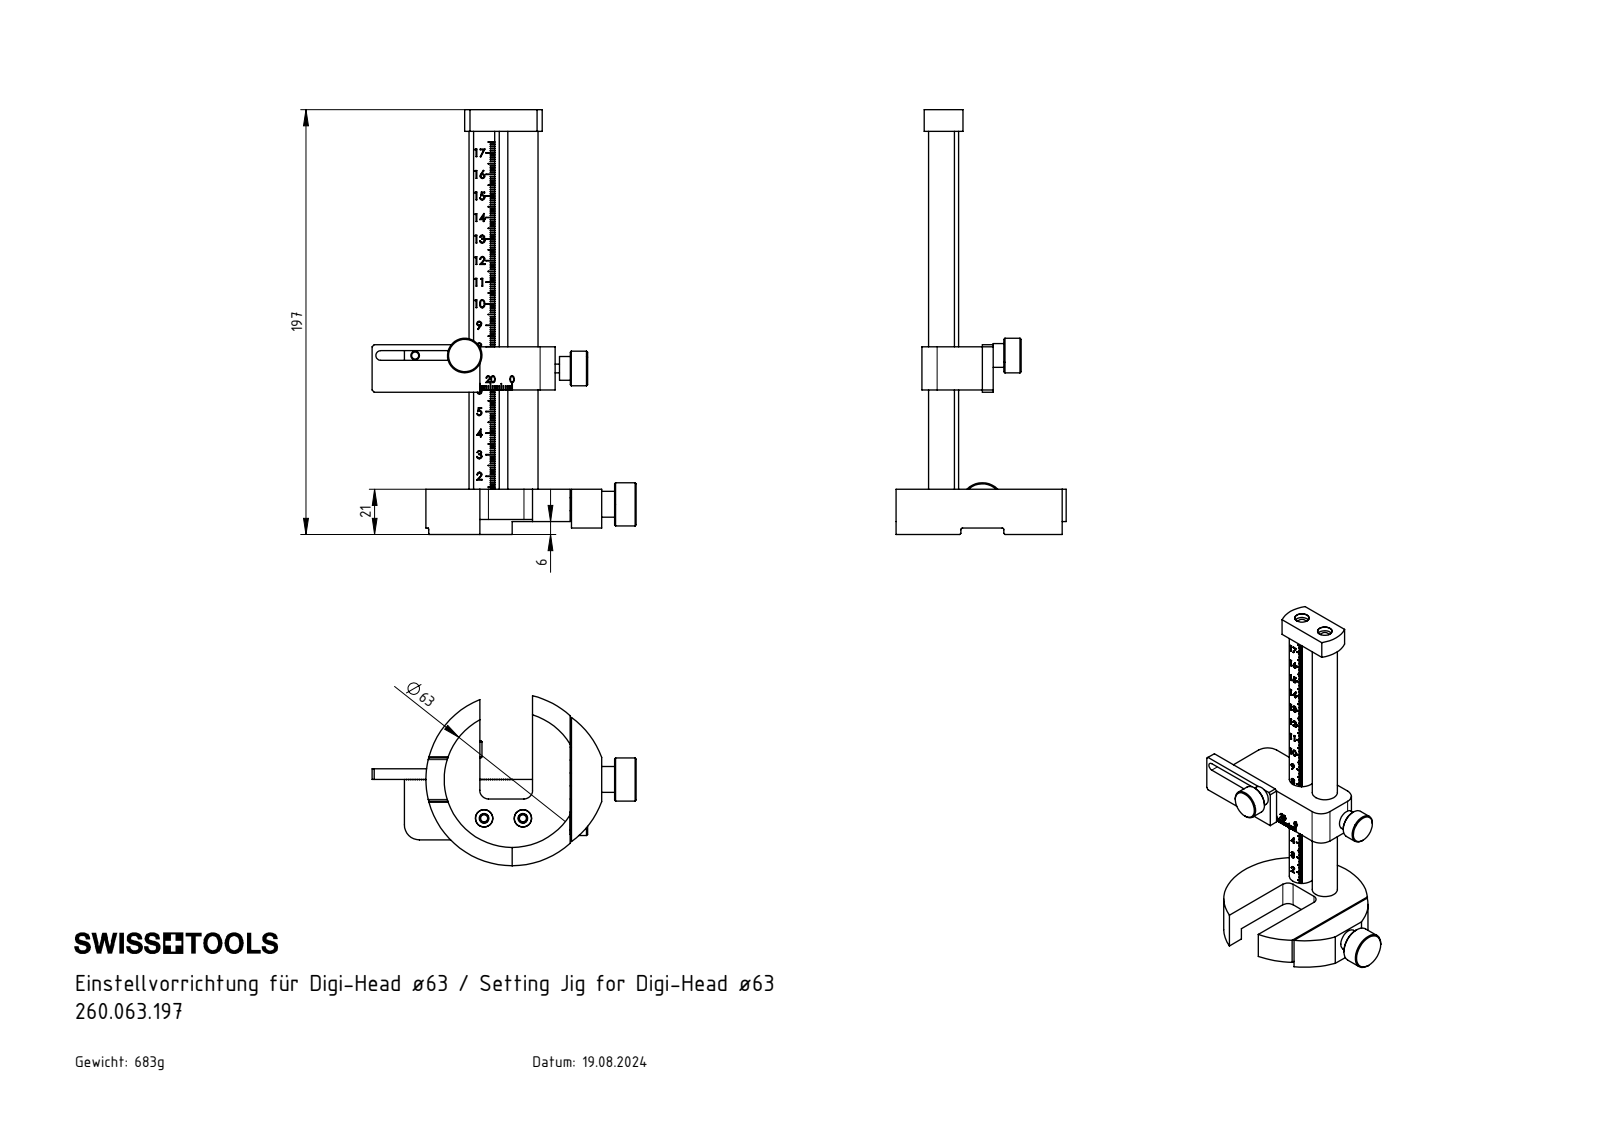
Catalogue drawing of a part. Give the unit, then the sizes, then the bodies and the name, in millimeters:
Units: millimetres
Overall size (bounding box): 197 × 122.55 × 78.86
Round holes (diameter × count): ⌀3.3 ×5, ⌀4.5 ×2, ⌀6 ×2, ⌀8 ×2, ⌀14 ×2, ⌀5 ×1, ⌀6.5 ×1
Round bosses / shafts (diameter × count): ⌀16 ×2, ⌀11 ×2, ⌀4 ×2, ⌀20 ×1, ⌀12 ×1, ⌀6 ×1
Partial cylindrical surfaces — rounded edges, fillets, slot ends (radius × count): R7 ×3, R40 ×3, R0.8 ×2, R2.25 ×2, R4 ×2, R18 ×1, R31.5 ×1
Main face-to-face distances: 14, 18, 5, 15, 13, 66, 60, 20, 46, 7
Hole centre spacings: 12, 18, 23, 24, 63.29, 65.52, 69.78
Volume: 160 976 mm³ · Surface area: 54 536 mm²
Bodies: 12 solids, 1655 faces (1298 planar, 100 cylindrical, 257 other)
Part name (STEP PRODUCT): A-Voreinstellung-Raendel-20; A-Voreinstellung-Raendel-16-M4; VA6-ER1.080.021_B; VA5-ER7.022.050_A (+7 more)
STEP written by: SolidWorks 2022 (AUTOMOTIVE_DESIGN)
